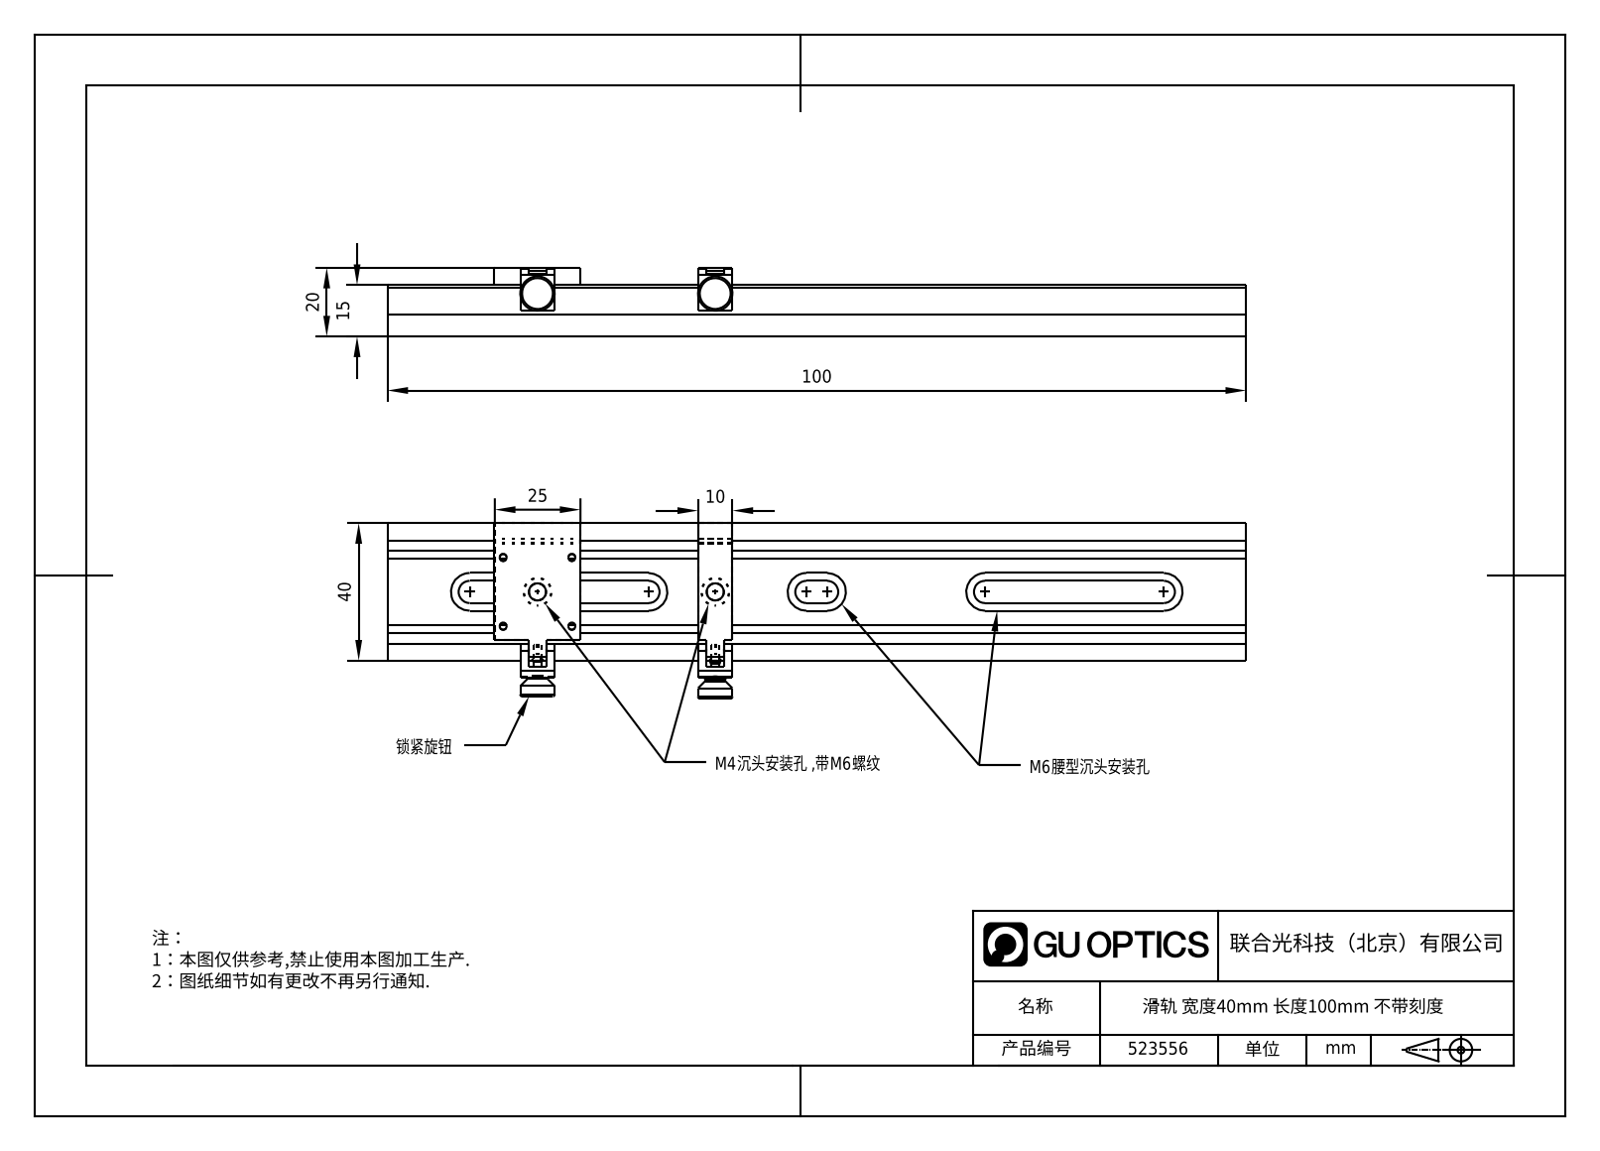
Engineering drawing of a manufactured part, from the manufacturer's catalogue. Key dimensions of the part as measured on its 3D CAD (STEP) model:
Part name (STEP PRODUCT): 4.2.1.2_H40G-100
STEP written by: SolidWorks 2021 (CONFIG_CONTROL_DESIGN)
Units: millimetres
Bodies: 0 solids, 149 faces (88 planar, 47 cylindrical, 14 other)
Overall size (bounding box): 100 × 51.03 × 20
Round holes (diameter × count): ⌀2.05 ×4, ⌀5 ×2, ⌀8 ×2, ⌀1.5 ×1
Round bosses / shafts (diameter × count): ⌀10 ×2, ⌀6 ×2
Partial cylindrical surfaces — rounded edges, fillets, slot ends (radius × count): R3.25 ×4, R5.5 ×4, R2.5 ×1, R4.5 ×1, R12.5 ×1
Main face-to-face distances: 6, 14.5, 5, 8.5, 0.5, 15, 19.5, 13.5, 6.5, 20
Hole centre spacings: 14.14, 20, 28.28, 31.43, 50.79, 39.8
